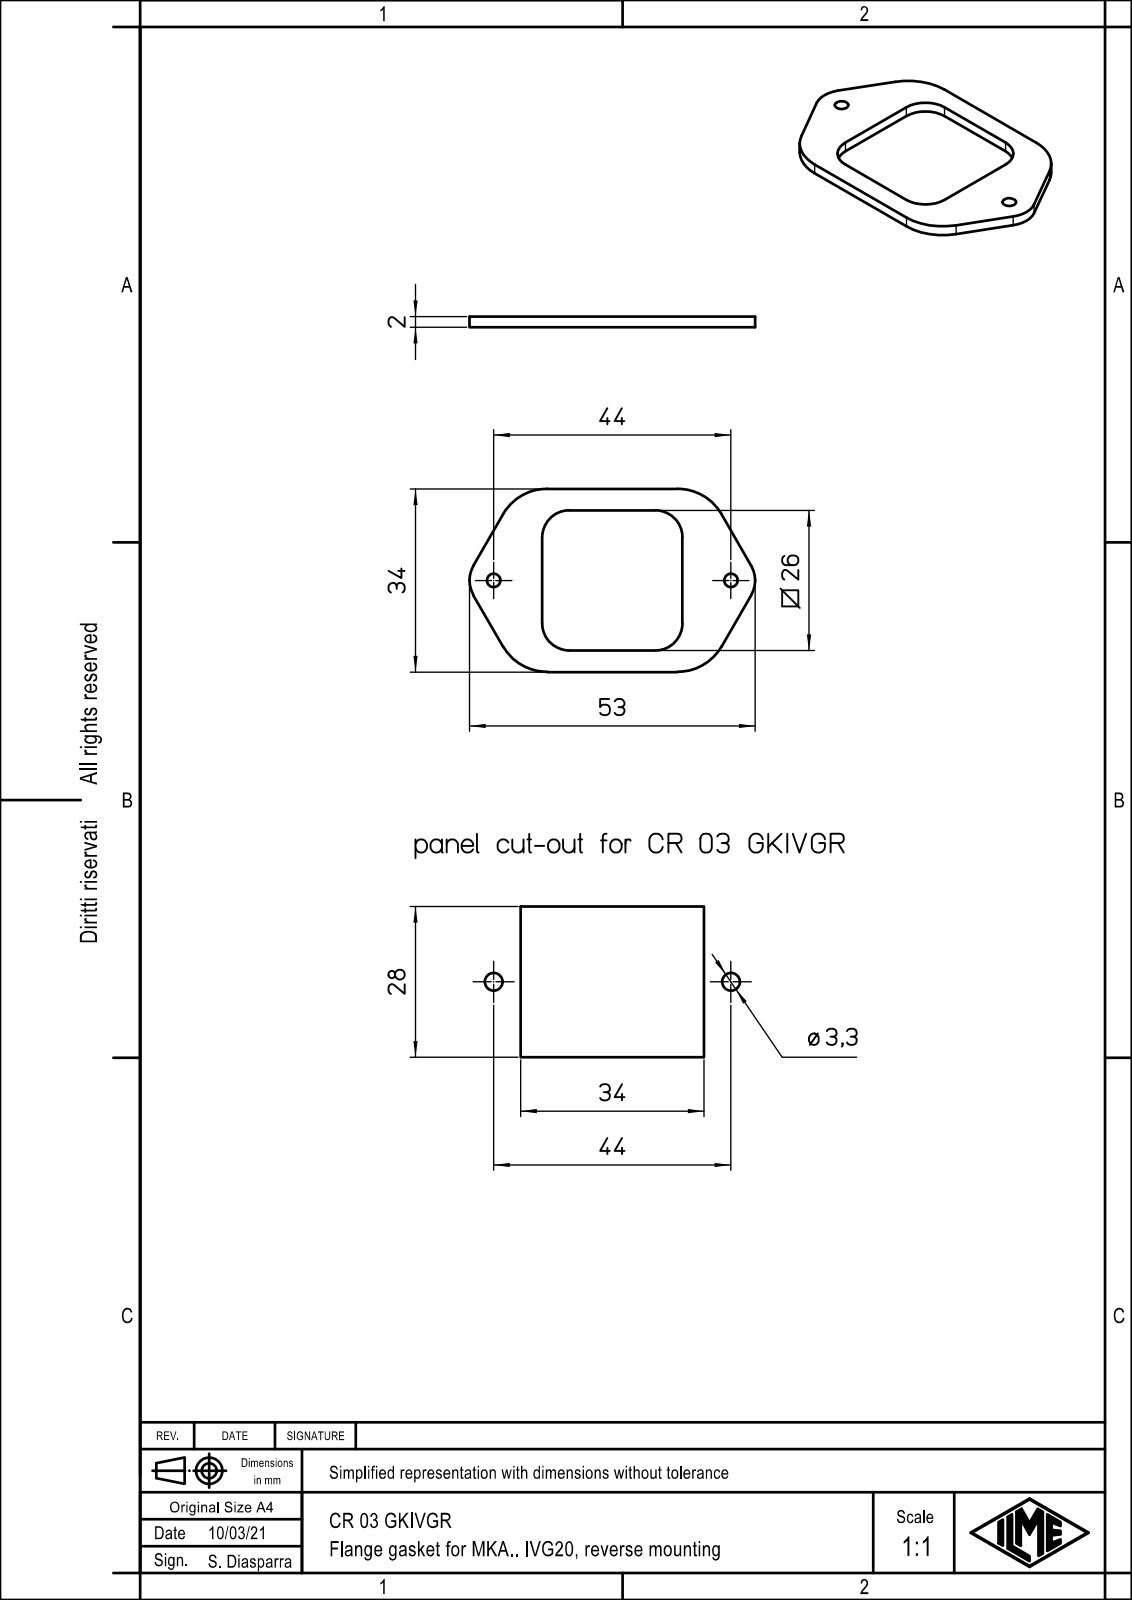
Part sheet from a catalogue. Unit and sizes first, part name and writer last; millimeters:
Units: millimetres
Overall size (bounding box): 53 × 34 × 2
Round holes (diameter × count): ⌀2.5 ×2
Partial cylindrical surfaces — rounded edges, fillets, slot ends (radius × count): R5 ×4, R9.5 ×4, R5.5 ×2
Main face-to-face distances: 2, 4, 30, 26, 34, 47.38
Hole centre spacings: 44
Volume: 1 678 mm³ · Surface area: 2 187 mm²
Bodies: 1 solid, 26 faces (12 planar, 14 cylindrical, 0 other)
Part name (STEP PRODUCT): CR_03_GKIVGR
STEP written by: Creo Elements/Direct Modeling 20.1B 02-Apr-2019 (C) Parametric Technology GmbH (AUTOMOTIVE_DESIGN)
